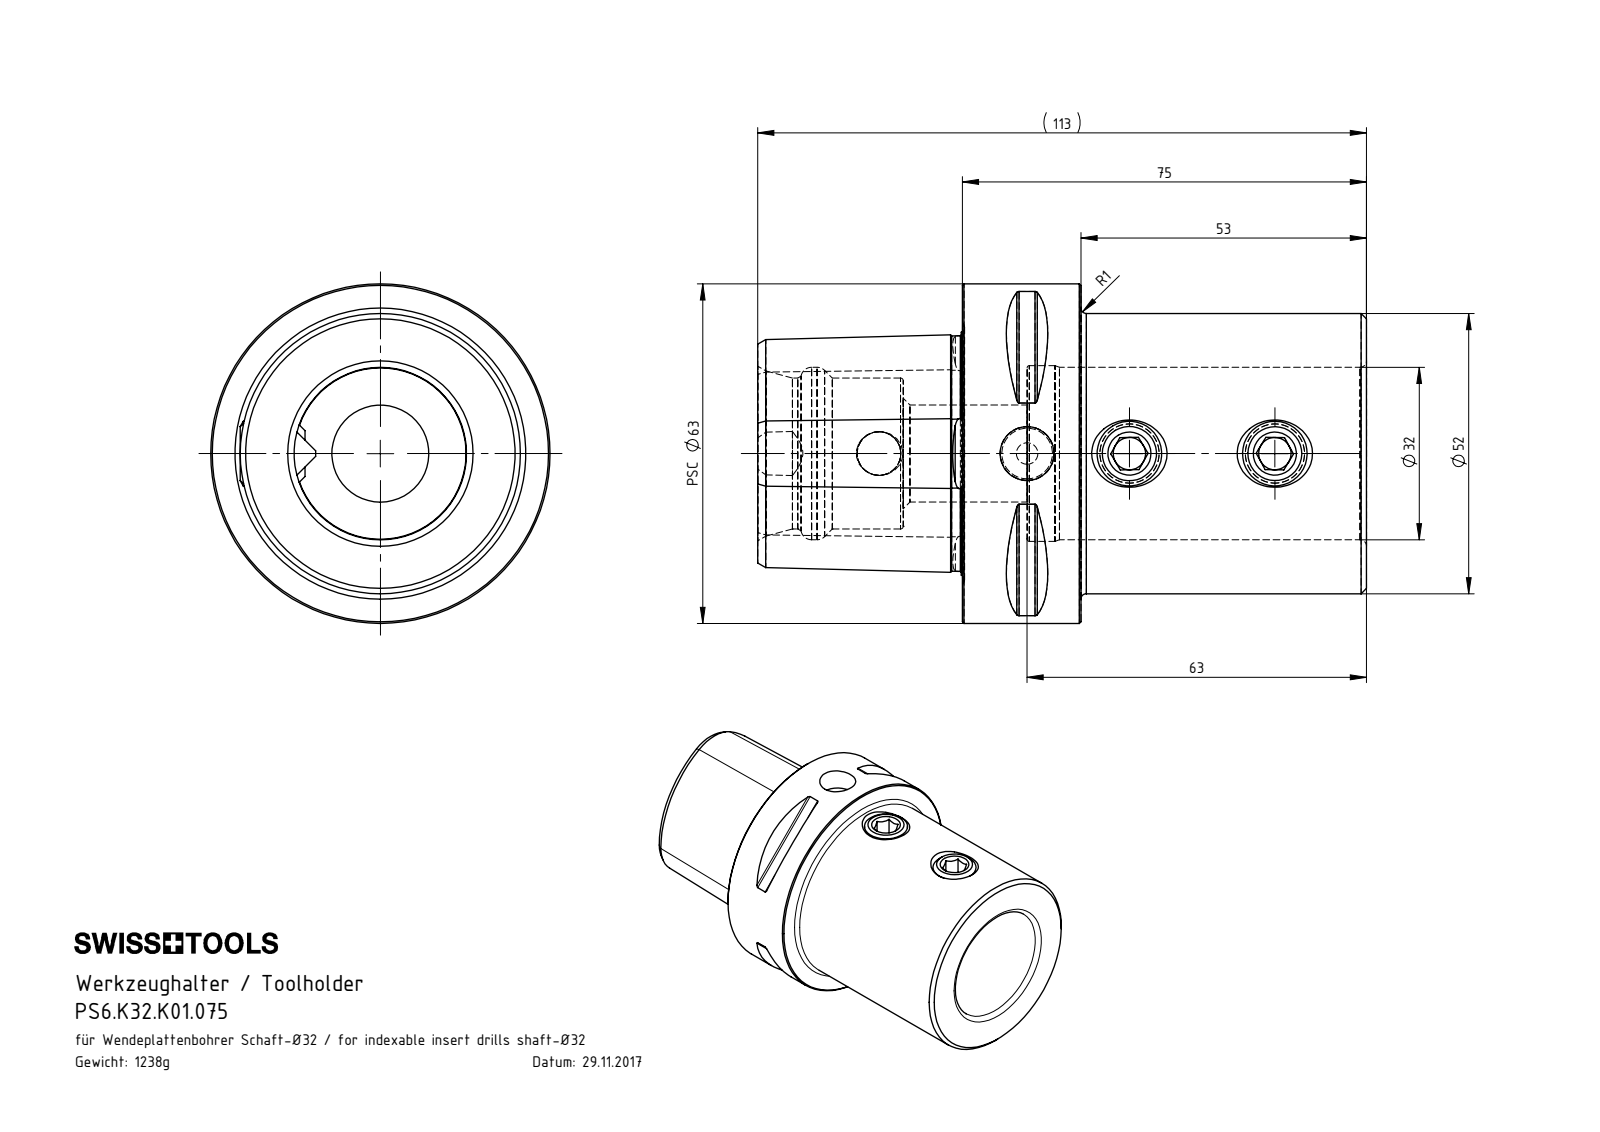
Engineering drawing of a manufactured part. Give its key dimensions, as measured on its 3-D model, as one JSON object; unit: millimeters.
{"part_name": "PS6-K32.K01.075_C; PS6.K32.K01.075; K32-ER2.012.014; K32-ER1.012.012_M12x12", "step_written_by": "SolidWorks 2017 (AUTOMOTIVE_DESIGN)", "units": "millimeters", "bodies": {"solids": 3, "faces": 202, "planar": 50, "cylindrical": 45, "other": 107}, "overall_size": [113, 63, 63], "volume_mm3": 157980, "surface_area_mm2": 36074, "round_holes": [[6, 2], [8.1, 2], [11, 2], [10, 1], [18, 1], [28, 1], [32, 1], [32.6, 1]], "round_bosses_or_shafts": [[12, 2], [63, 1], [52, 1]], "partial_cylinders_radius": [[0.5, 8], [6, 1]], "face_to_face_distances": [75, 22, 53, 12, 10, 63, 38, 50, 60, 113], "hole_center_spacings": [19, 27, 27.5, 46, 46.5, 73.5]}
